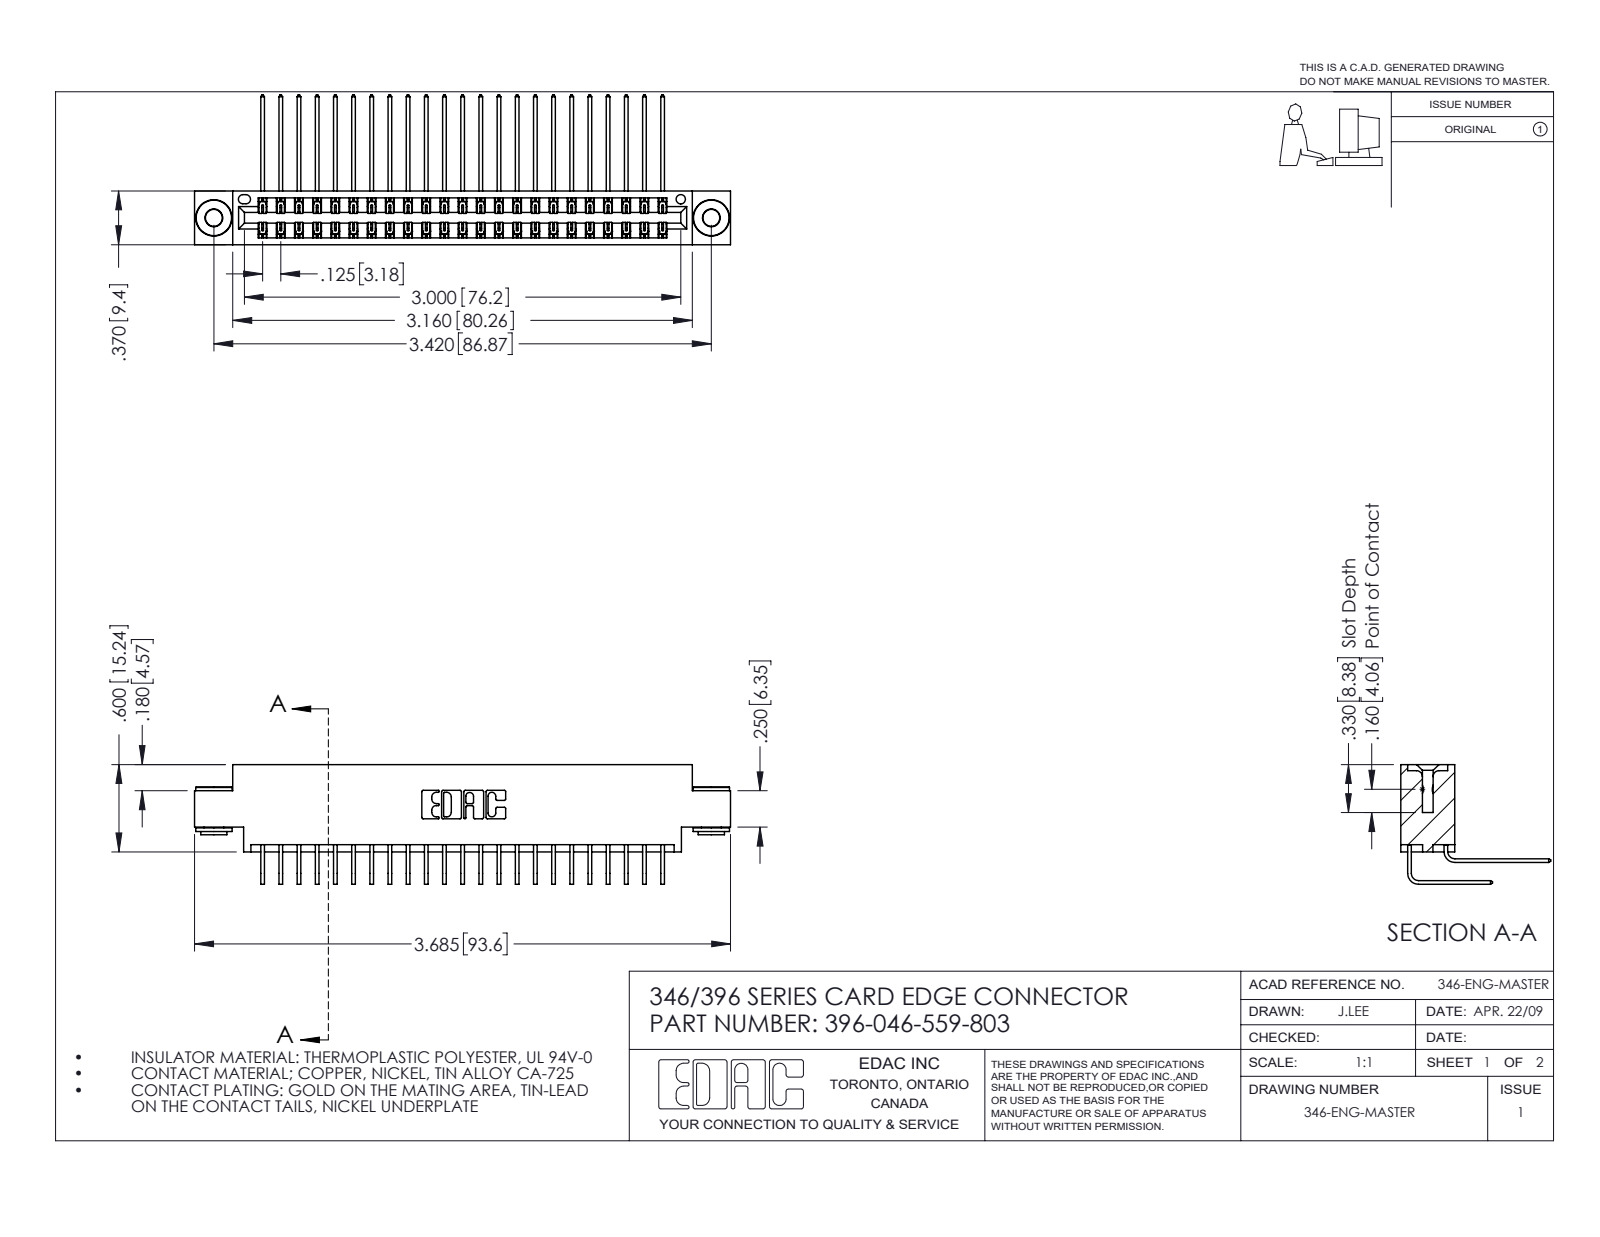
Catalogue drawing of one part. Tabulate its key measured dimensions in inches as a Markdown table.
| quantity | value |
| --- | --- |
| part name | 396-046-559-803; 345-292-001_558 559 Tail - 1; 345-250-002_345-250-002-102; 345-292-001_559 Tail - 2 (+1 more) |
| STEP written by | SolidWorks 2016 (CONFIG_CONTROL_DESIGN) |
| units | inches |
| bodies | 49 solids, 2648 faces (1792 planar, 848 cylindrical, 8 other) |
| overall size | 3.685 × 1.03 × 0.823 |
| volume | 0.556 in³ |
| surface area | 21.53 in² |
| round holes (diameter × count) | 0.116 × 2, 0.156 × 2, 0.064 × 1 |
| round bosses / shafts (diameter × count) | 0.25 × 2, 0.18 × 2, 0.136 × 2 |
| partial cylindrical surfaces (radius × count) | 0.006 × 69, 0.01 × 22, 0.007 × 6, 0.031 × 6, 0.026 × 3, 0.014 × 2, 0.022 × 2, 0.024 × 2 |
| main face-to-face distances | 0.048, 0.322, 0.025, 0.37, 0.25, 0.072, 0.298, 0.275, 0.15, 0.148 |
| hole center spacings | 0.246, 3.212, 3.42 |
